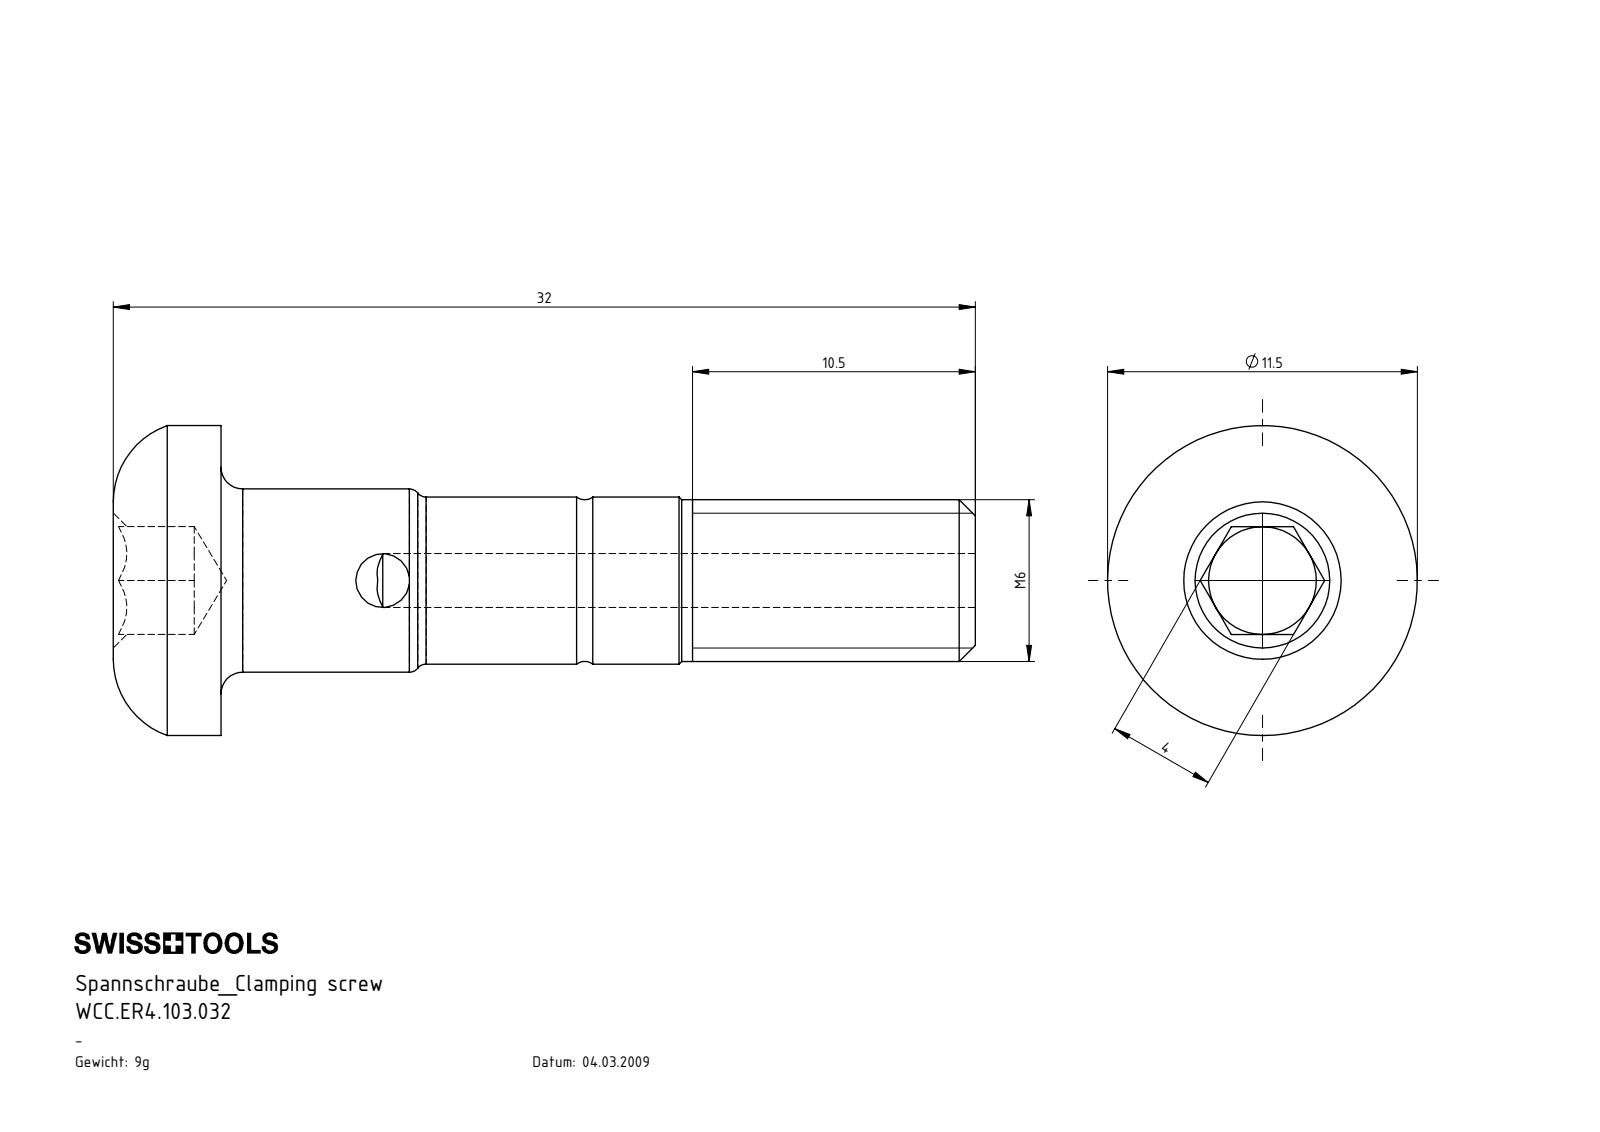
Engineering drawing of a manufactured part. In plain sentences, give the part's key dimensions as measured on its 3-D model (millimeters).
The part is named "WCC.ER4.103.032". Its 3-D file was written by "SolidWorks 2017 (AUTOMOTIVE_DESIGN)". It is 1 solid with 35 faces: 15 planar, 9 cylindrical and 11 other. Overall it measures 32 by 11.5 by 11.5 millimeters. Its volume is 1 095 cubic millimeters and its surface area 1 047 square millimeters. Round holes: 2 of diameter 2, 1 of diameter 4. Round bosses or shafts: 1 of diameter 11.5, 1 of diameter 6.8, 1 of diameter 6.2, 1 of diameter 6. The main face-to-face distances are 4, 28, 32, 3, 1, 29.
